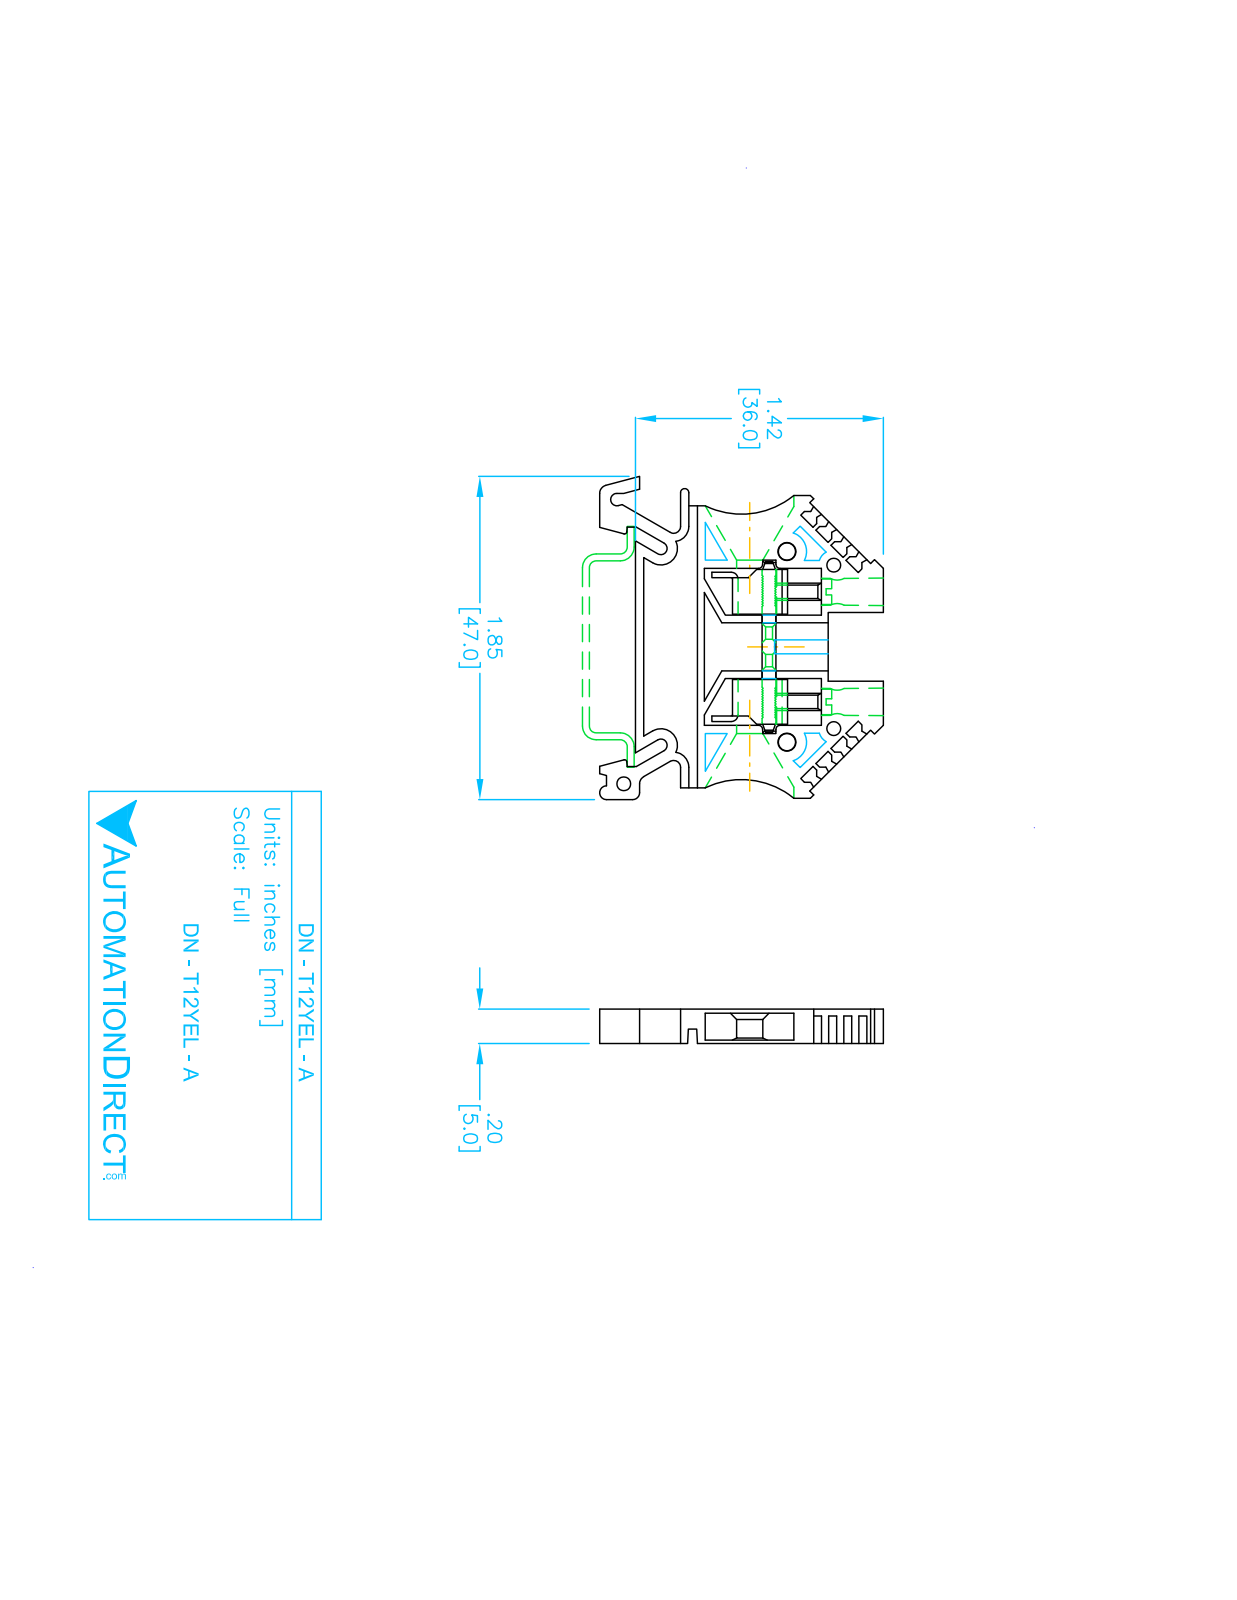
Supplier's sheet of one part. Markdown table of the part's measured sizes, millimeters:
| quantity | value |
| --- | --- |
| part name | DN-T12YEL-A |
| STEP written by | SolidWorks 2017 (AUTOMOTIVE_DESIGN) |
| units | millimeters |
| bodies | 1 solid, 169 faces (134 planar, 35 cylindrical, 0 other) |
| overall size | 47 × 41.2 × 5 |
| volume | 5 010 mm³ |
| surface area | 4 601 mm² |
| round holes (diameter × count) | 4.2 × 2, 2 × 1 |
| partial cylindrical surfaces (radius × count) | 1 × 4, 0.9 × 3, 0.3 × 2, 1.2 × 2, 2.2 × 2, 2.4 × 2, 12 × 2, 0.6 × 1 |
| main face-to-face distances | 4.8, 5, 2.2, 0.5, 2.7, 2.4, 2.9, 2.1, 2.6, 9 |
| hole center spacings | 15 |
